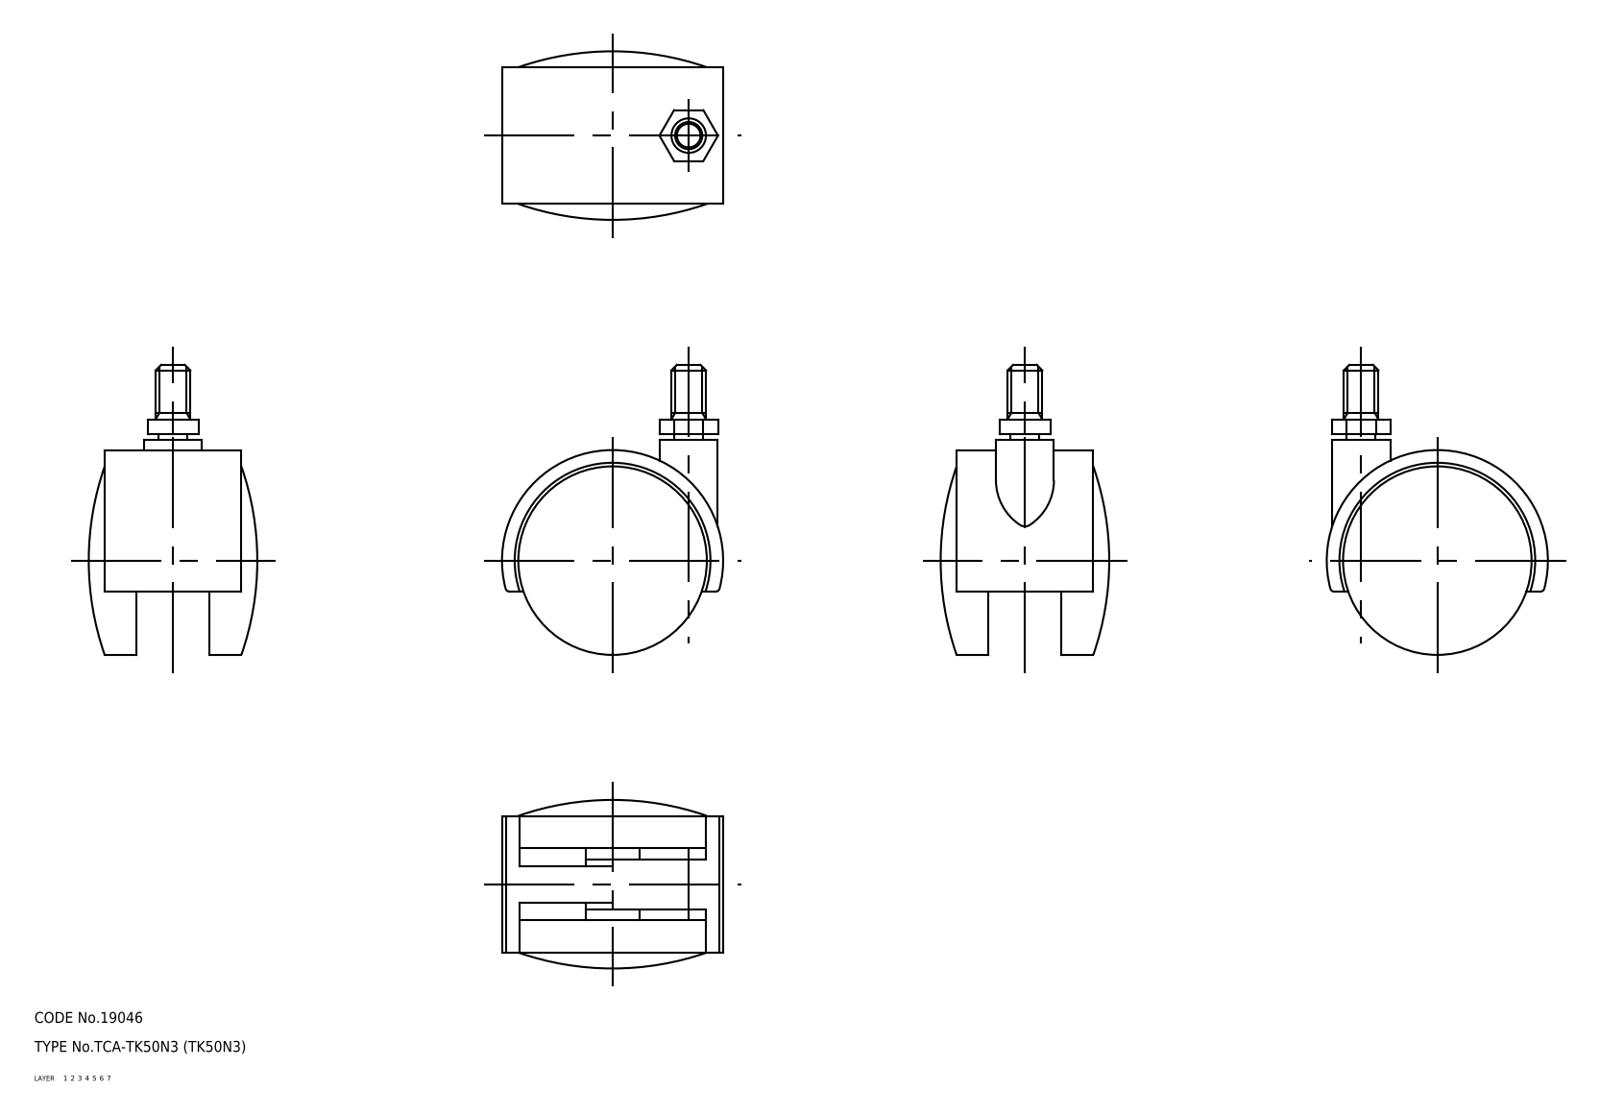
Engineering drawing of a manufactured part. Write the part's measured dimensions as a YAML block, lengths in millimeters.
part_name: "wheel; main shaft; TK50N3_4741_36"
step_written_by: "CADfix (AUTOMOTIVE_DESIGN)"
units: millimeters
bodies: {solids: 4, faces: 74, planar: 0, cylindrical: 0, other: 74}
overall_size: [80, 61, 46.5]
volume: 69803
surface_area: 28424
